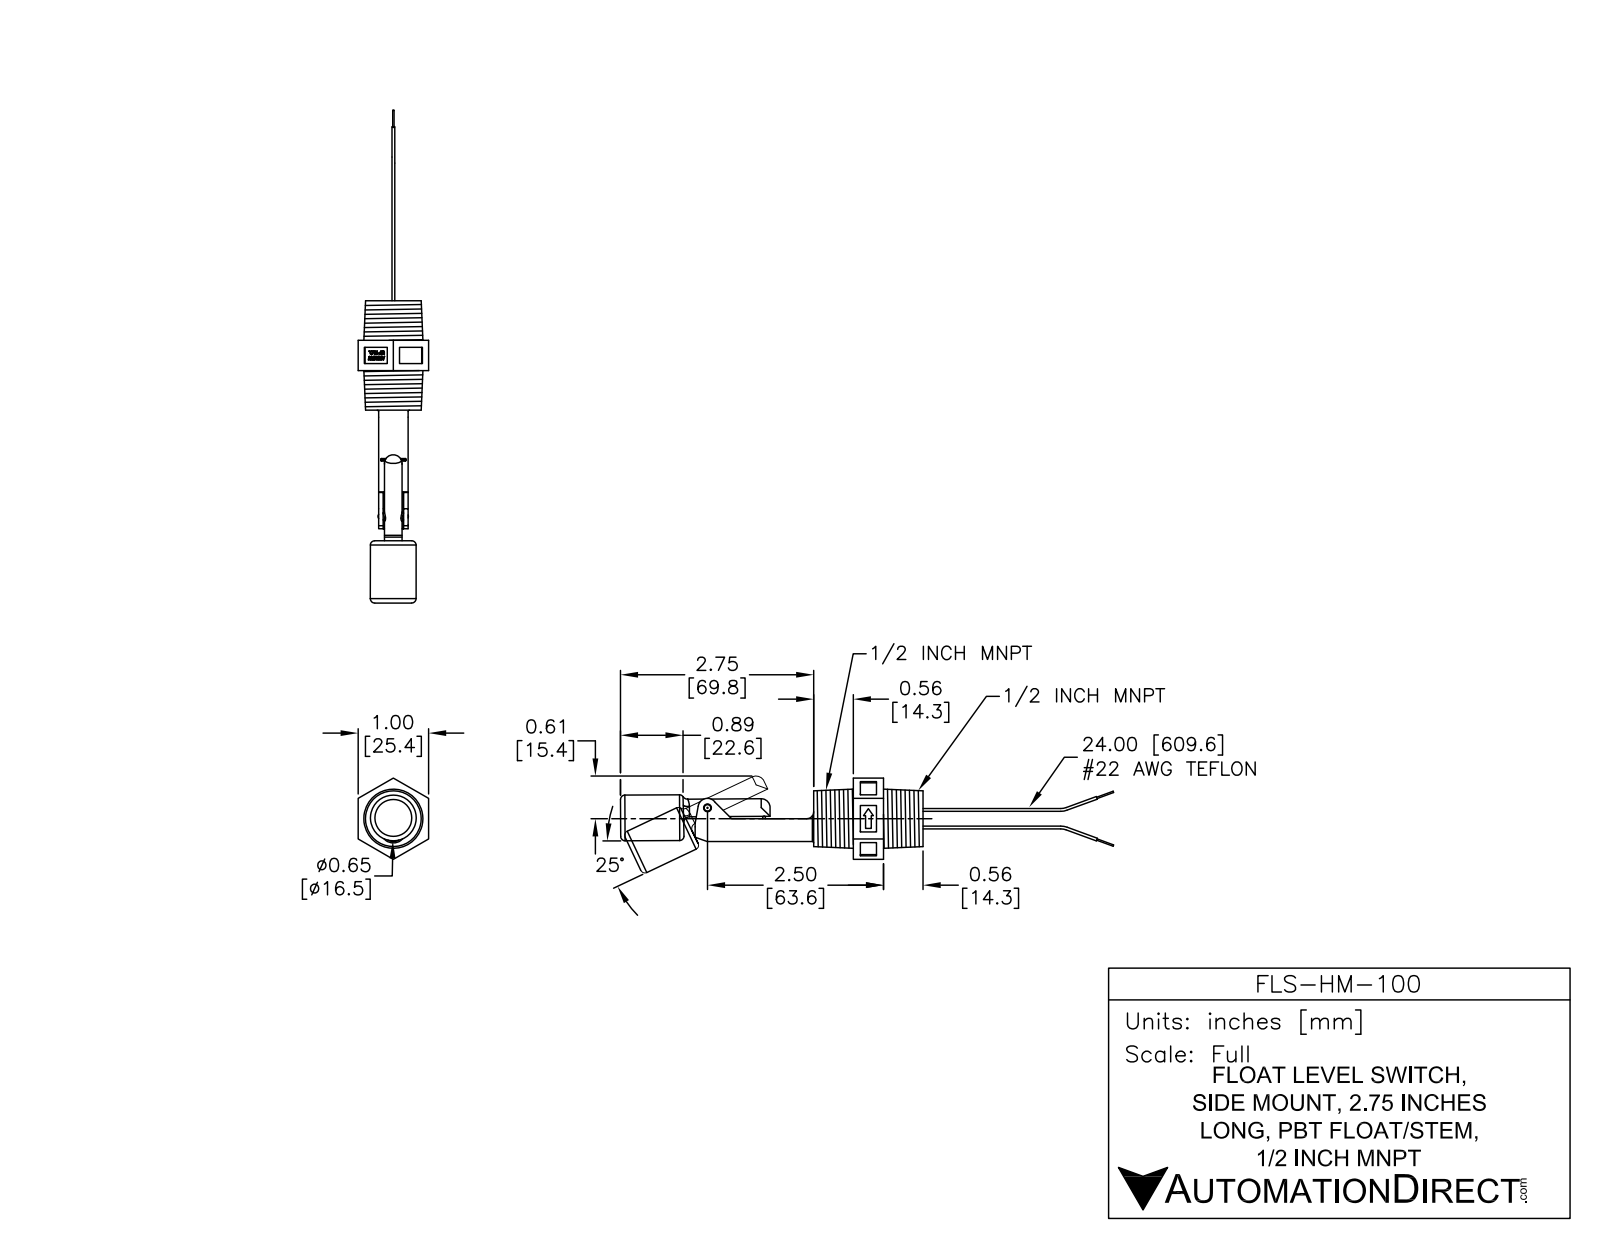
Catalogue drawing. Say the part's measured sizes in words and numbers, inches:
The part is named "FLS-HM-100". Its 3-D file was written by "SolidWorks 2013 (AUTOMOTIVE_DESIGN)". It is 6 solids with 163 faces: 88 planar, 41 cylindrical and 34 other. Overall it measures 7.019 by 1.155 by 1 inches. Its volume is 1.445 cubic inches and its surface area 14.78 square inches. Round holes: 1 of diameter 0.109. Round bosses or shafts: 4 of diameter 0.04, 2 of diameter 0.02, 1 of diameter 0.65, 1 of diameter 0.25, 1 of diameter 0.1. Partial cylindrical surfaces (rounded edges, fillets, slot ends): 8 of radius 0.01, 2 of radius 0.02, 2 of radius 0.067, 1 of radius 0.1, 1 of radius 0.125, 1 of radius 0.21. The main face-to-face distances are 0.43, 0.02, 0.98, 1, 0.563, 0.993, 1.513, 0.95, 0.52, 0.355.
